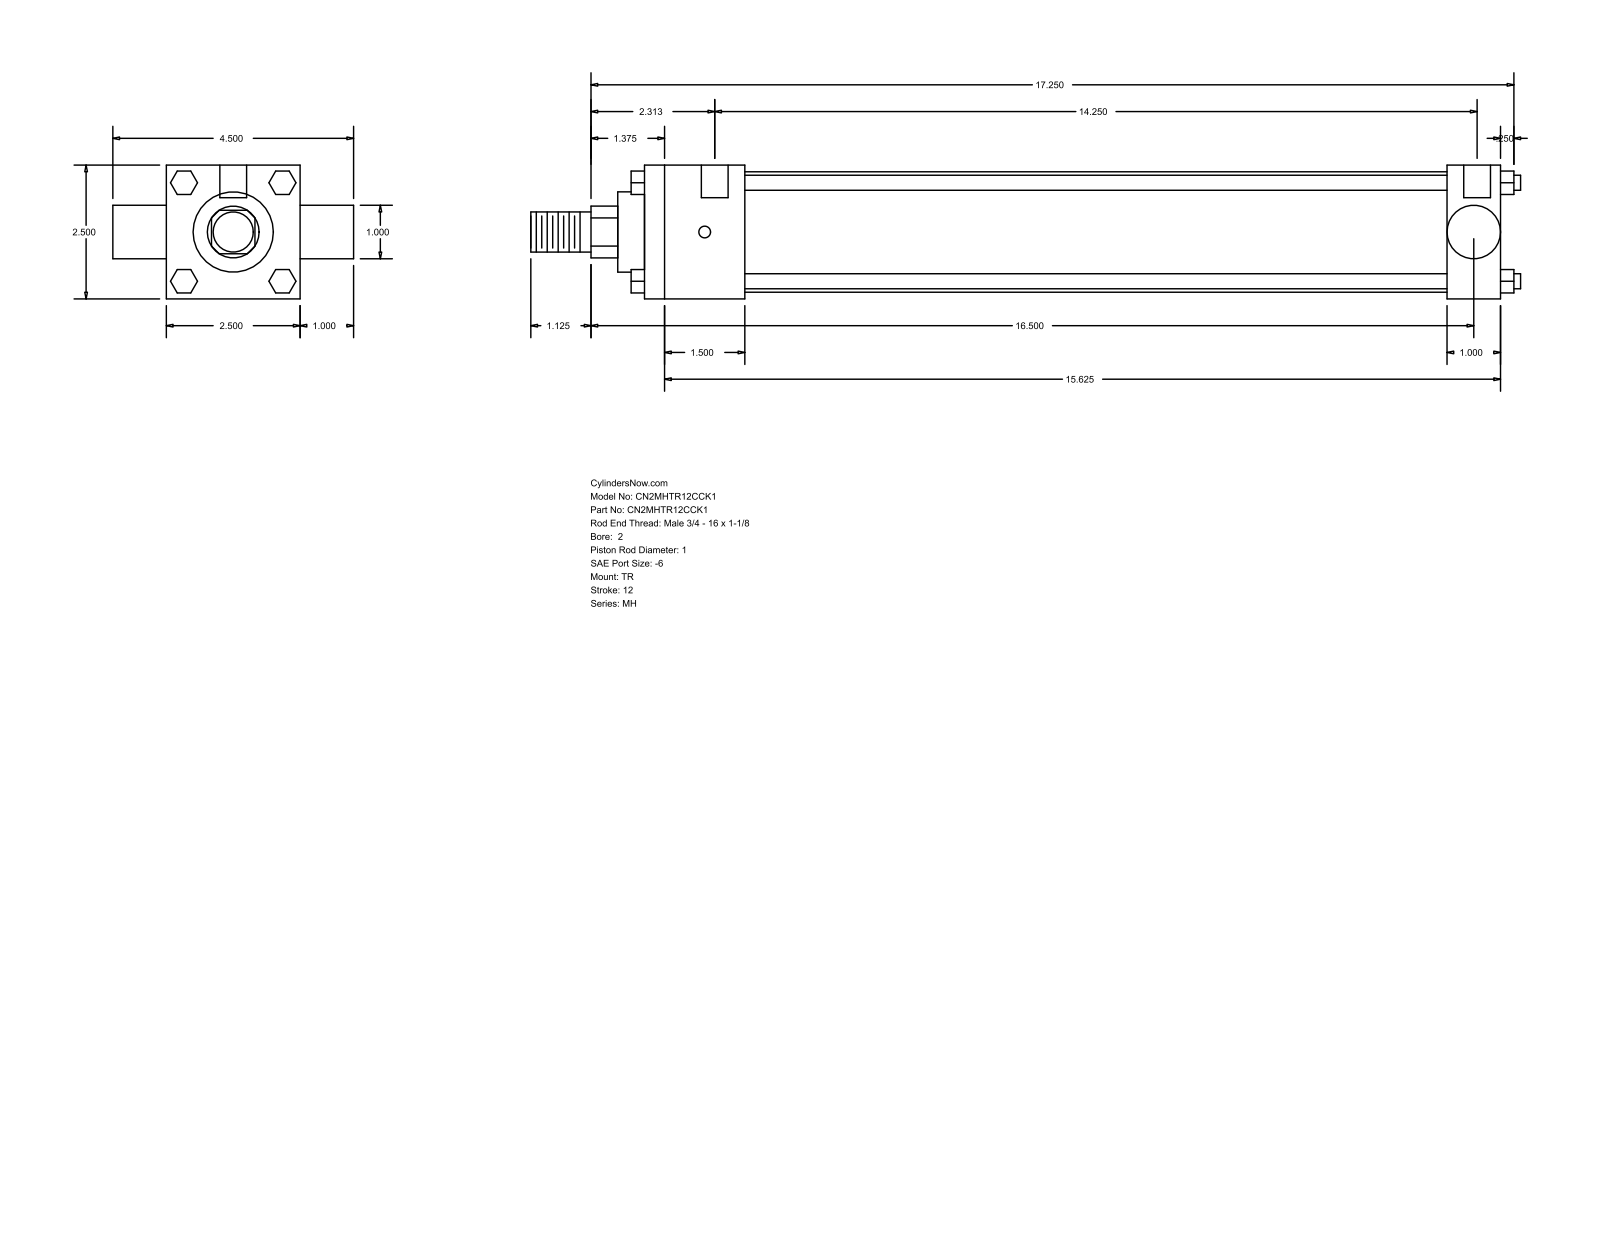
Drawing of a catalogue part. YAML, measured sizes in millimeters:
part_name: "MH_TR__0200_1"
step_written_by: "GSSL Pune (CONFIG_CONTROL_DESIGN)"
units: millimeters
bodies: {solids: 0, faces: 120, planar: 92, cylindrical: 28, other: 0}
overall_size: [469.9, 114.3, 63.5]
round_holes:
  - {diameter: 5.56, count: 3}
  - {diameter: 12.7, count: 2}
round_bosses_or_shafts:
  - {diameter: 7.14, count: 4}
  - {diameter: 57.15, count: 1}
  - {diameter: 38.1, count: 1}
  - {diameter: 25.4, count: 1}
  - {diameter: 25.35, count: 1}
  - {diameter: 19.05, count: 1}
partial_cylinders:
  - {radius: 12.29, count: 1}
face_to_face_distances: [63.5, 406.4, 25.4, 47.63, 381, 333.37, 358.77, 88.9, 419.1, 6.35]
hole_center_spacings: [3.17, 4.76, 361.95, 365.12, 366.71, 369.88]
